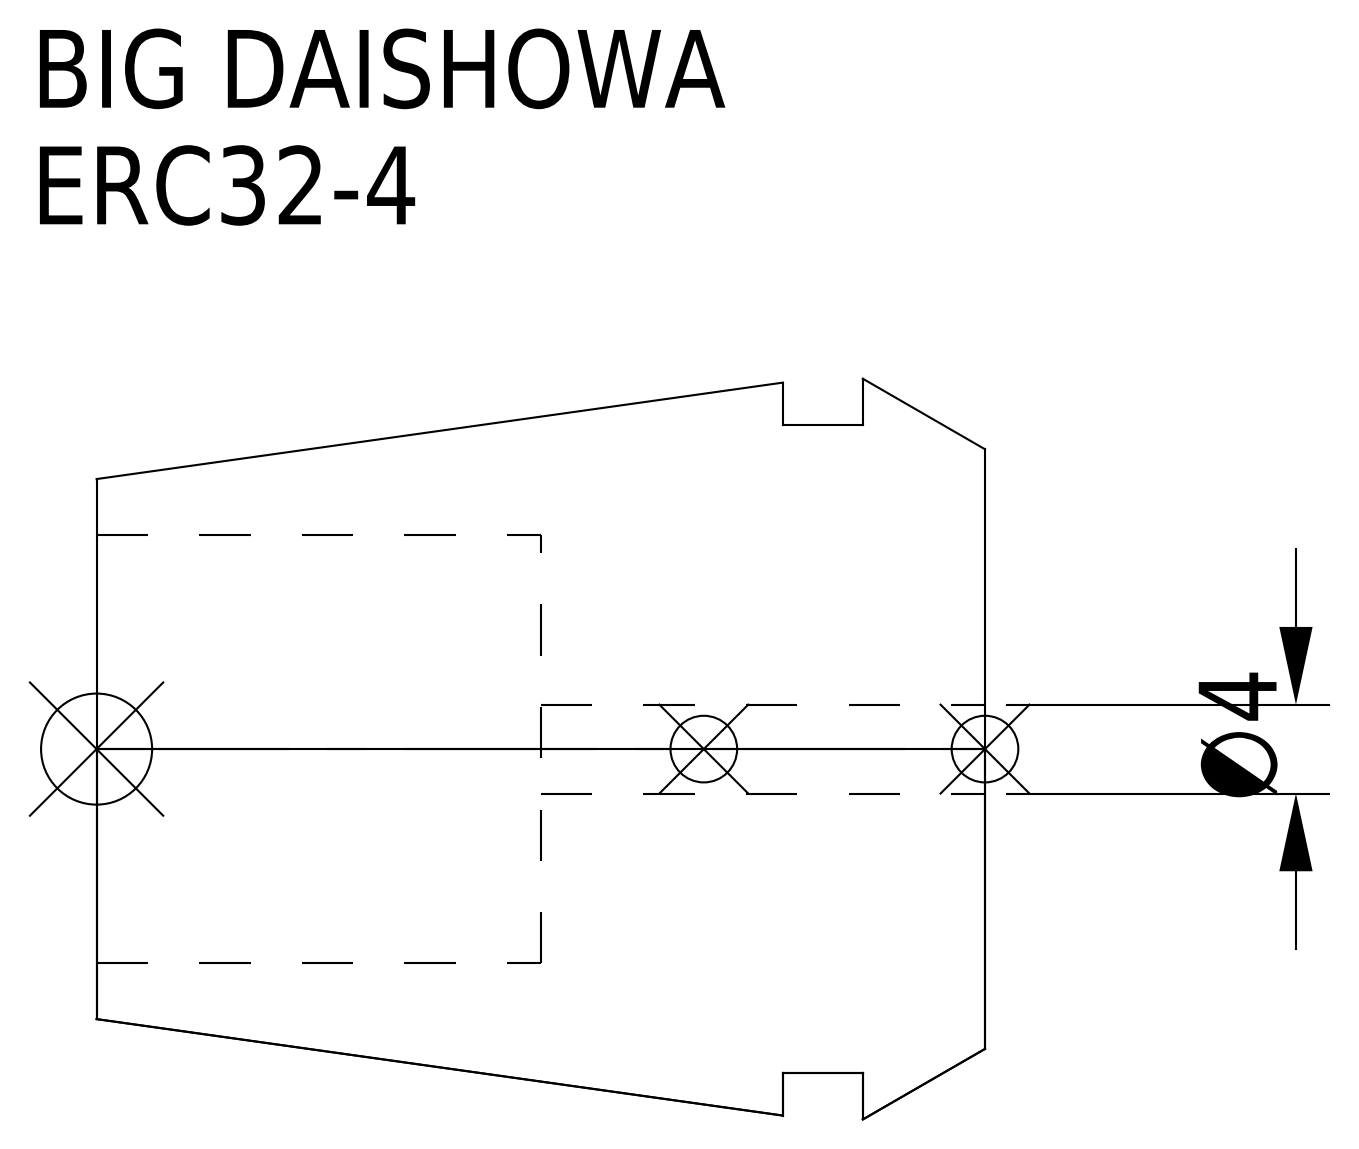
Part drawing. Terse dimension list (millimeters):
name: ERC32-4
written by: CREO PARAMETRIC BY PTC INC, 2016380 (AUTOMOTIVE_DESIGN)
unit: mm
bodies: 1 solid, 15 faces (5 planar, 6 cylindrical, 4 other)
size: 40 × 33.35 × 33.35
volume: 20 340 mm³; area: 6 607 mm²
holes: 1× ⌀4, 1× ⌀19.3
bosses: 1× ⌀29.2
face distances: 20, 5.5, 14.5, 9.1, 3.6, 10.9, 40, 34.5, 30.9
